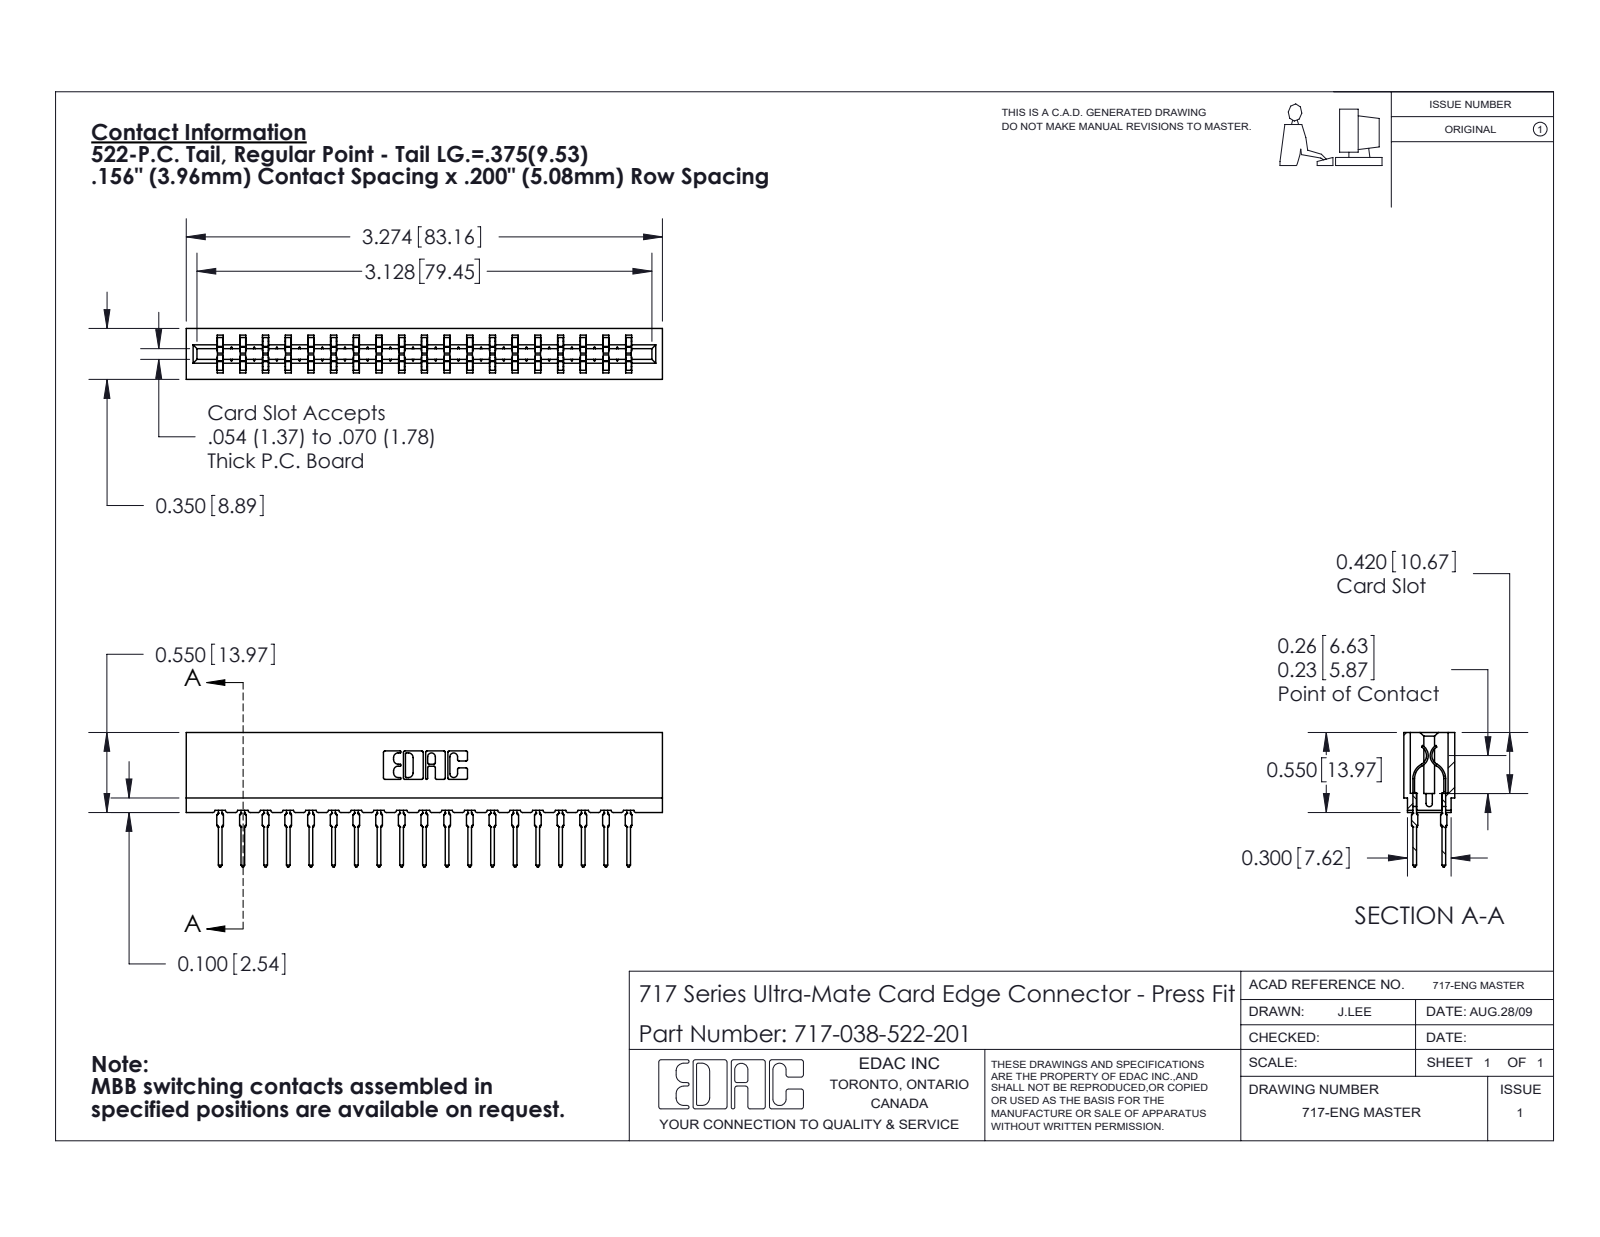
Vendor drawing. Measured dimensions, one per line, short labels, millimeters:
name: 745-292-001_522; 717-038-522-201; 717 Part_Insulator Option - 06
written by: SolidWorks 2020 (CONFIG_CONTROL_DESIGN)
unit: mm
bodies: 39 solids, 3514 faces (1821 planar, 705 cylindrical, 988 other)
size: 83.2 × 23.5 × 8.9
volume: 7 340 mm³; area: 11 070 mm²
rounds: 76× R0.5, 38× R0.4, 22× R0.3, 8× R0.1, 8× R0.3, 6× R0.2, 6× R0.8, 3× R0.7
face distances: 5.4, 3.5, 8.9, 4, 1.6, 7.3, 1.9, 3.8, 15.8, 1.9
